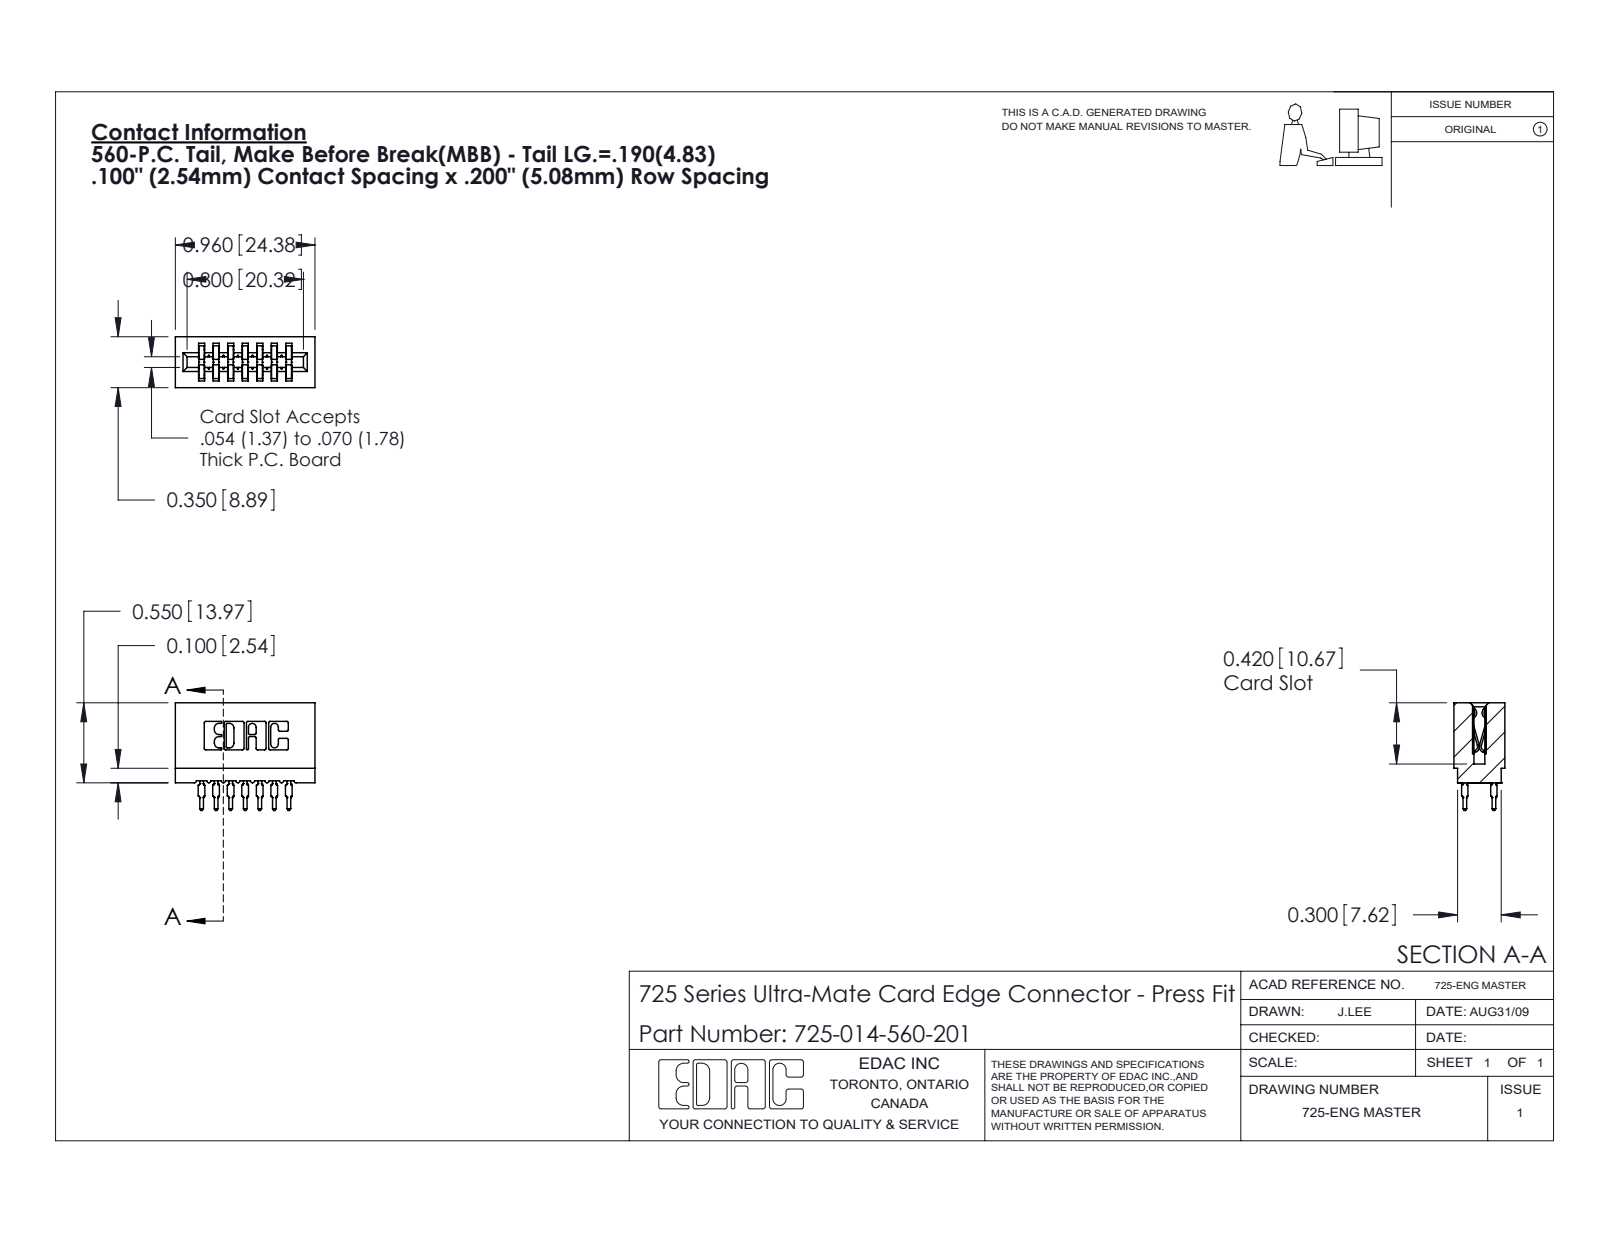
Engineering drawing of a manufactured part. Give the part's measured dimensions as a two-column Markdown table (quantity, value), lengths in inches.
| quantity | value |
| --- | --- |
| part name | 745-292-001_560; 725-014-560-201; 725 Part_Insulator Option - 01 |
| STEP written by | SolidWorks 2020 (CONFIG_CONTROL_DESIGN) |
| units | inches |
| bodies | 15 solids, 1474 faces (769 planar, 341 cylindrical, 364 other) |
| overall size | 0.96 × 0.741 × 0.35 |
| volume | 0.132 in³ |
| surface area | 6.26 in² |
| partial cylindrical surfaces (radius × count) | 0.021 × 28, 0.01 × 22, 0.015 × 14, 0.005 × 8, 0.011 × 8, 0.007 × 6, 0.031 × 6, 0.026 × 3 |
| main face-to-face distances | 0.1, 0.2, 0.3, 0.042, 0.4, 0.142, 0.058, 0.242, 0.158, 0.5 |
